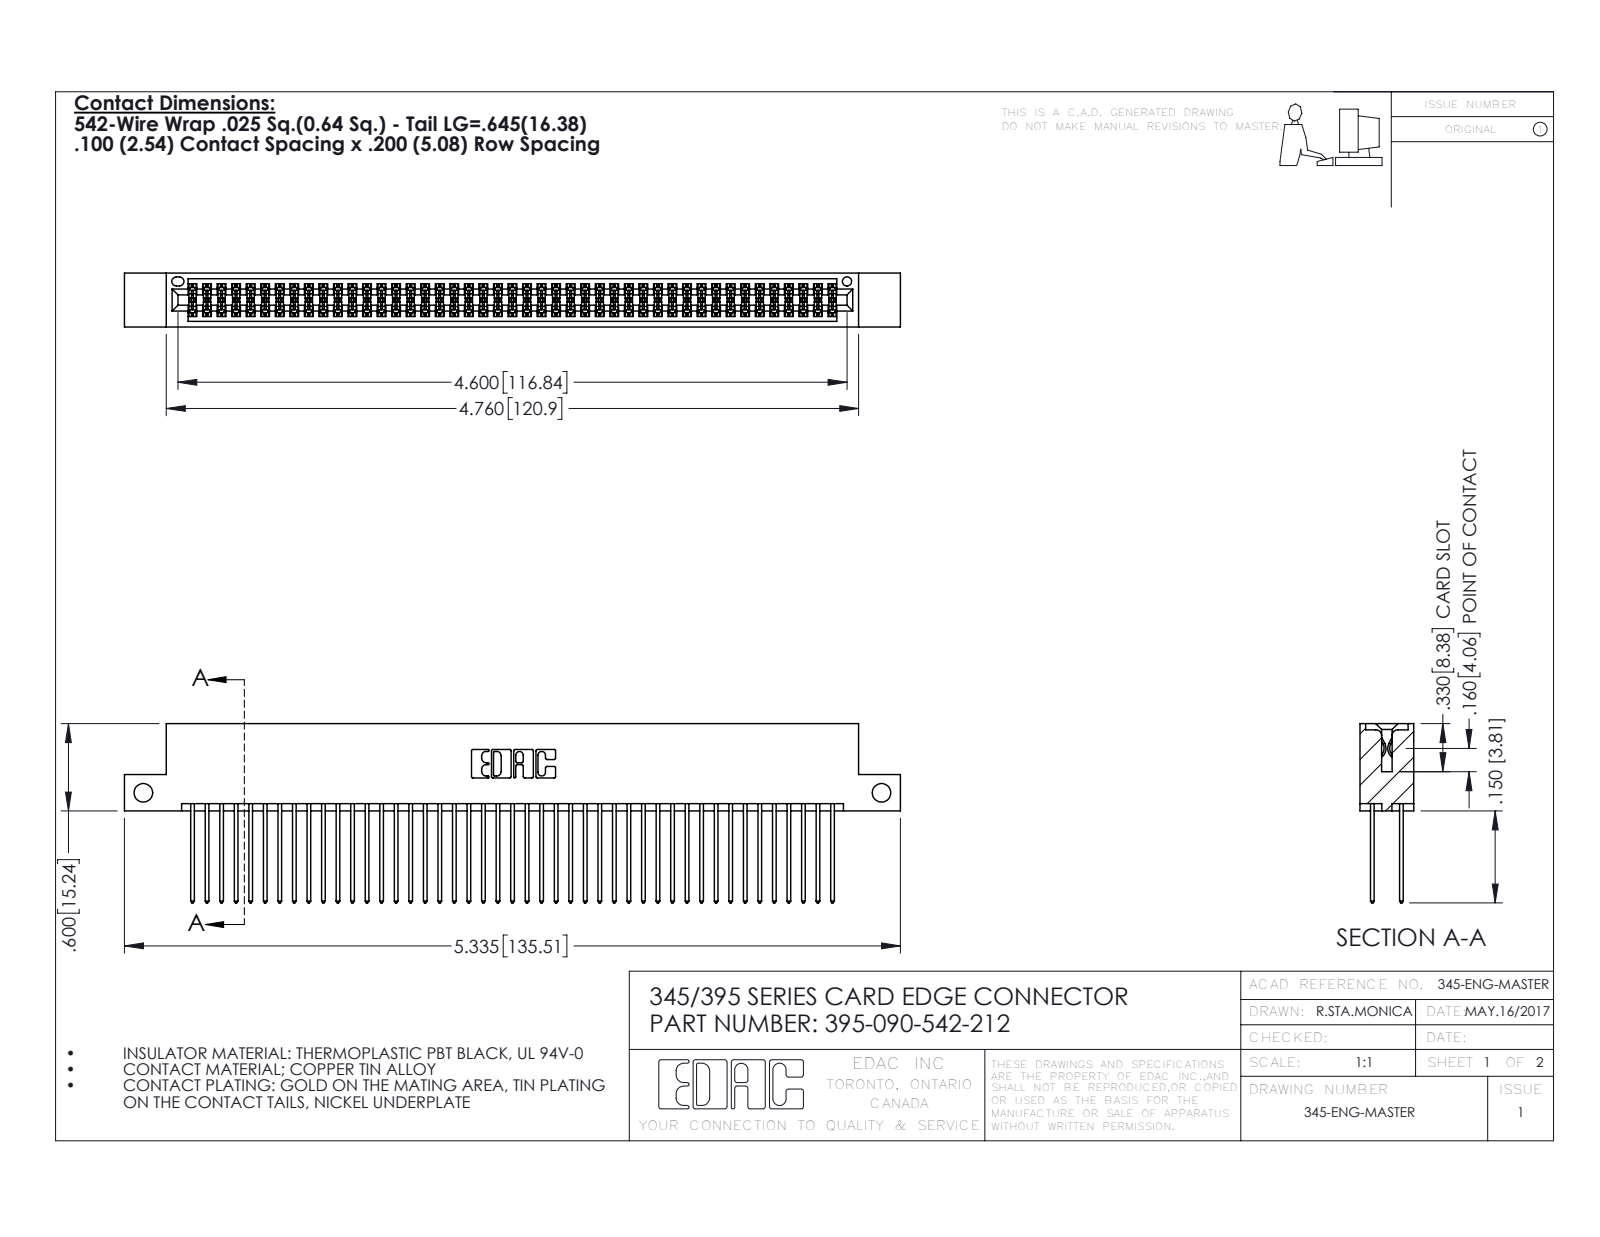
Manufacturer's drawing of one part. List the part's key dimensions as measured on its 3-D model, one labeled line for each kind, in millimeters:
Part name (STEP PRODUCT): 345-292-001_345-293-142; 395-090-542-212; 345 Part_Flush Mounting Lugs - Side Mount
STEP written by: SolidWorks 2016 (CONFIG_CONTROL_DESIGN)
Units: millimetres
Bodies: 91 solids, 4626 faces (3050 planar, 1576 cylindrical, 0 other)
Overall size (bounding box): 135.5 × 31.3 × 9.4
Volume: 13 500 mm³ · Surface area: 21 870 mm²
Round holes (diameter × count): ⌀3.3 ×2, ⌀1.6 ×1
Partial cylindrical surfaces — rounded edges, fillets, slot ends (radius × count): R0.2 ×135, R0.3 ×90, R0.3 ×22, R0.2 ×6, R0.8 ×6, R0.7 ×3, R0.4 ×2, R0.5 ×2
Main face-to-face distances: 7.6, 1.8, 5.1, 2.5, 6.9, 0.6, 5.7, 9.4, 4.4, 3.8
Hole centre spacings: 128.9
